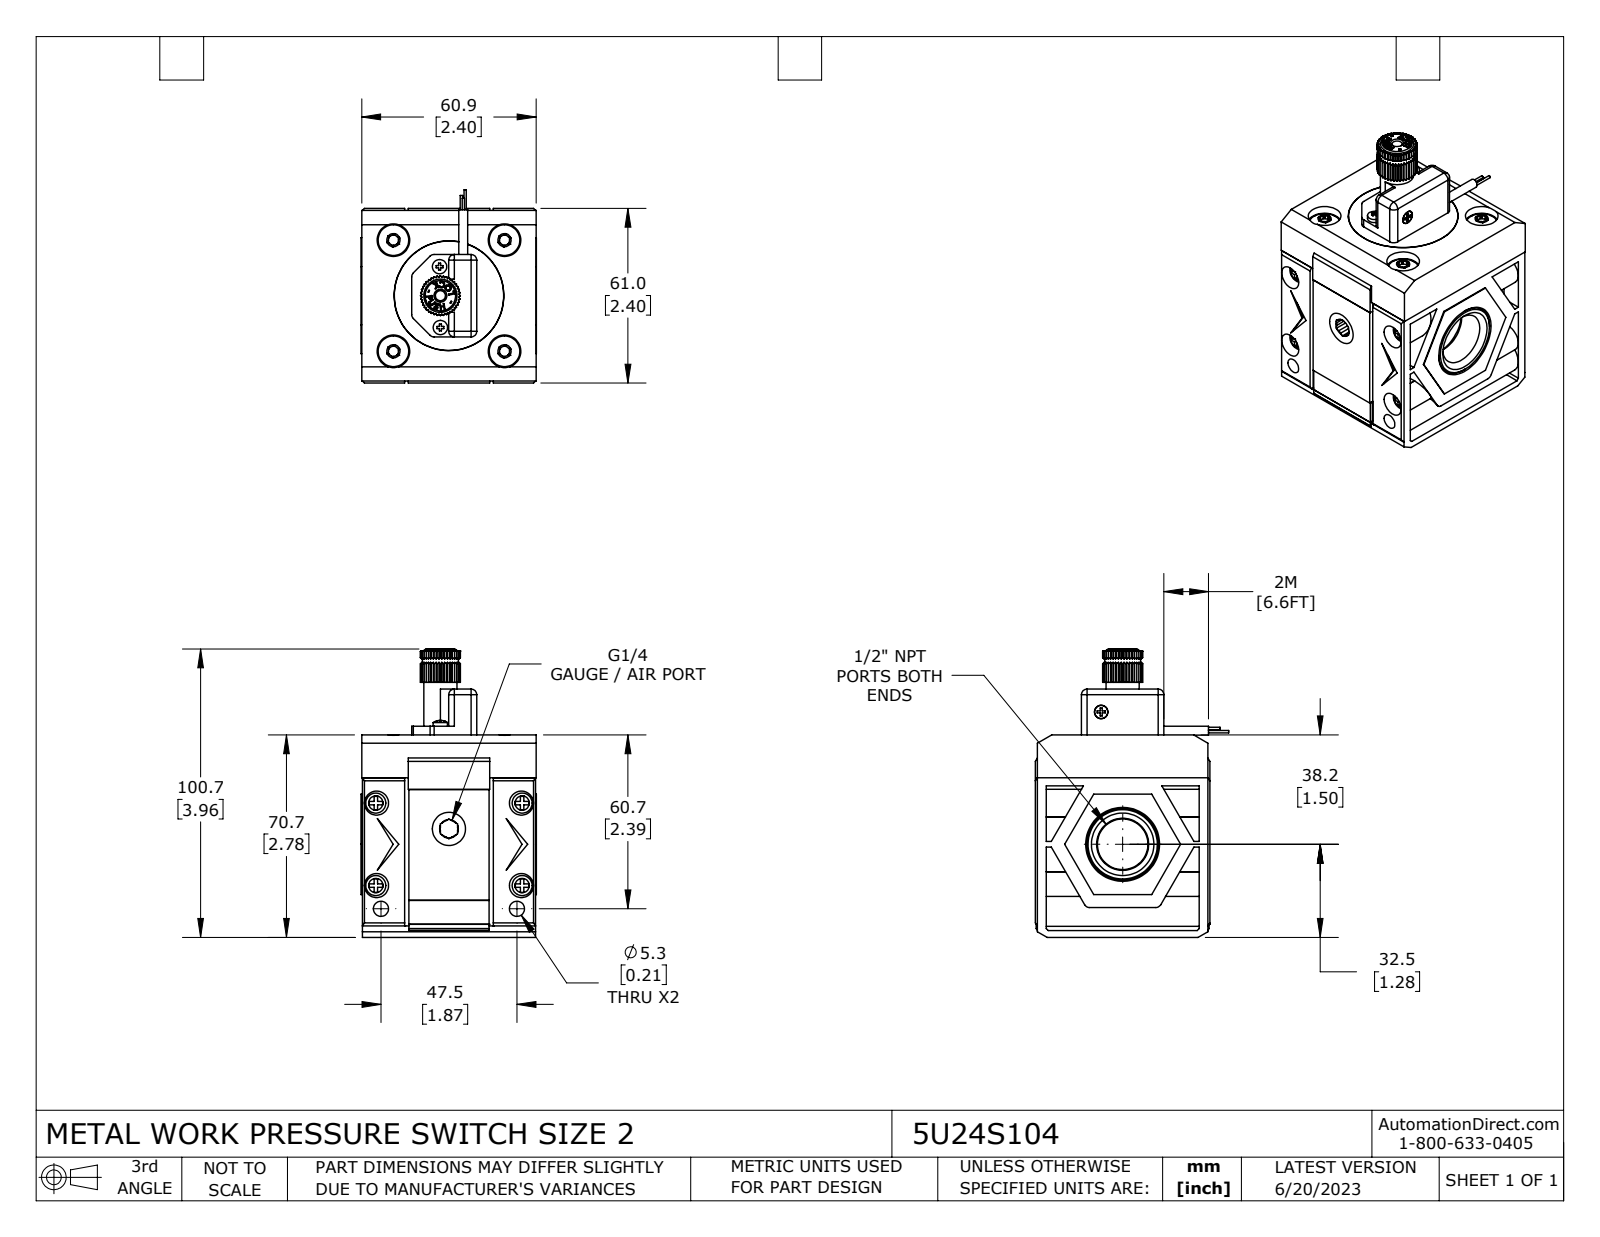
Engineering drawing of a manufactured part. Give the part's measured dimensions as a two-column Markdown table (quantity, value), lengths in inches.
| quantity | value |
| --- | --- |
| part name | 5U24S104 |
| STEP written by | SolidWorks 2021 (CONFIG_CONTROL_DESIGN) |
| units | inches |
| bodies | 13 solids, 1217 faces (682 planar, 343 cylindrical, 192 other) |
| overall size | 3.965 × 2.657 × 2.411 |
| volume | 12.66 in³ |
| surface area | 110.5 in² |
| round holes (diameter × count) | 0.128 × 4, 0.165 × 4, 0.331 × 4, 0.449 × 4, 0.209 × 2, 0.071 × 1, 0.457 × 1, 1.25 × 1, 1.508 × 1 |
| round bosses / shafts (diameter × count) | 0.276 × 4, 0.189 × 4, 0.15 × 4, 0.031 × 3, 0.197 × 2, 1.504 × 1, 1.248 × 1, 1.035 × 1 |
| partial cylindrical surfaces (radius × count) | 0.011 × 28, 0.079 × 14, 0.069 × 4, 0.191 × 4, 0.242 × 2, 0.008 × 1, 0.009 × 1, 0.009 × 1 |
| main face-to-face distances | 2.39, 0.094, 2.193, 2.098, 2.402, 0.028, 0.591, 1.799, 0.299, 2.783 |
| hole center spacings | 1.08, 1.528, 0.325, 1.057, 1.134, 1.265, 1.443, 1.454 |
